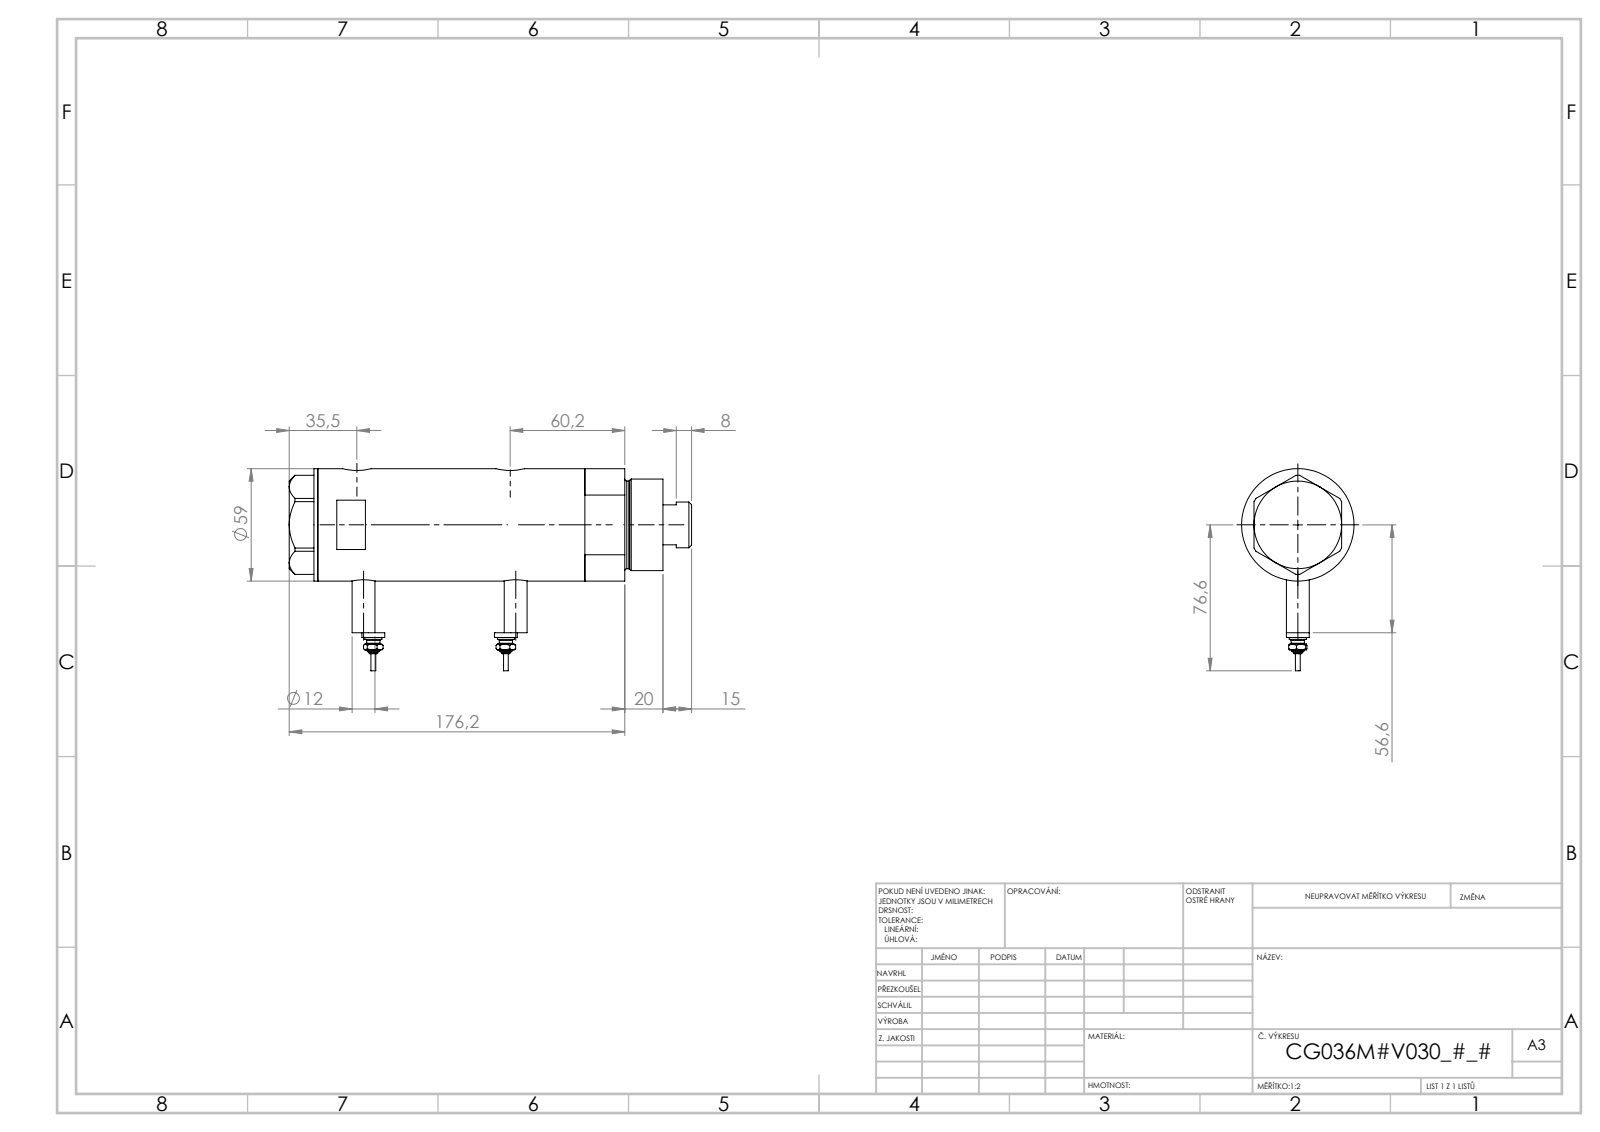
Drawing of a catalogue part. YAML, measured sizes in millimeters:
part_name: "Switch; V270CG_FRONT; V270CG_VC; V270CG_MIDDLE (+1 more)"
step_written_by: "SolidWorks 2019 (CONFIG_CONTROL_DESIGN)"
units: millimeters
bodies: {solids: 6, faces: 212, planar: 79, cylindrical: 69, other: 64}
overall_size: [211.2, 106.1, 59]
volume: 494998
surface_area: 103444
round_holes:
  - {diameter: 9.73, count: 2}
  - {diameter: 12.5, count: 2}
  - {diameter: 15, count: 2}
  - {diameter: 8.5, count: 1}
  - {diameter: 25, count: 1}
  - {diameter: 26.5, count: 1}
  - {diameter: 36, count: 1}
  - {diameter: 40, count: 1}
  - {diameter: 52, count: 1}
round_bosses_or_shafts:
  - {diameter: 12, count: 4}
  - {diameter: 9, count: 2}
  - {diameter: 7, count: 2}
  - {diameter: 4.5, count: 2}
  - {diameter: 2.5, count: 2}
  - {diameter: 59, count: 1}
  - {diameter: 48, count: 1}
  - {diameter: 46, count: 1}
face_to_face_distances: [102.2, 23.5, 78.7, 15, 38.5, 117.2, 2, 196.2, 181.2, 157.7]
hole_center_spacings: [2.9, 3.5, 77, 79.9, 80.5, 83.4]
